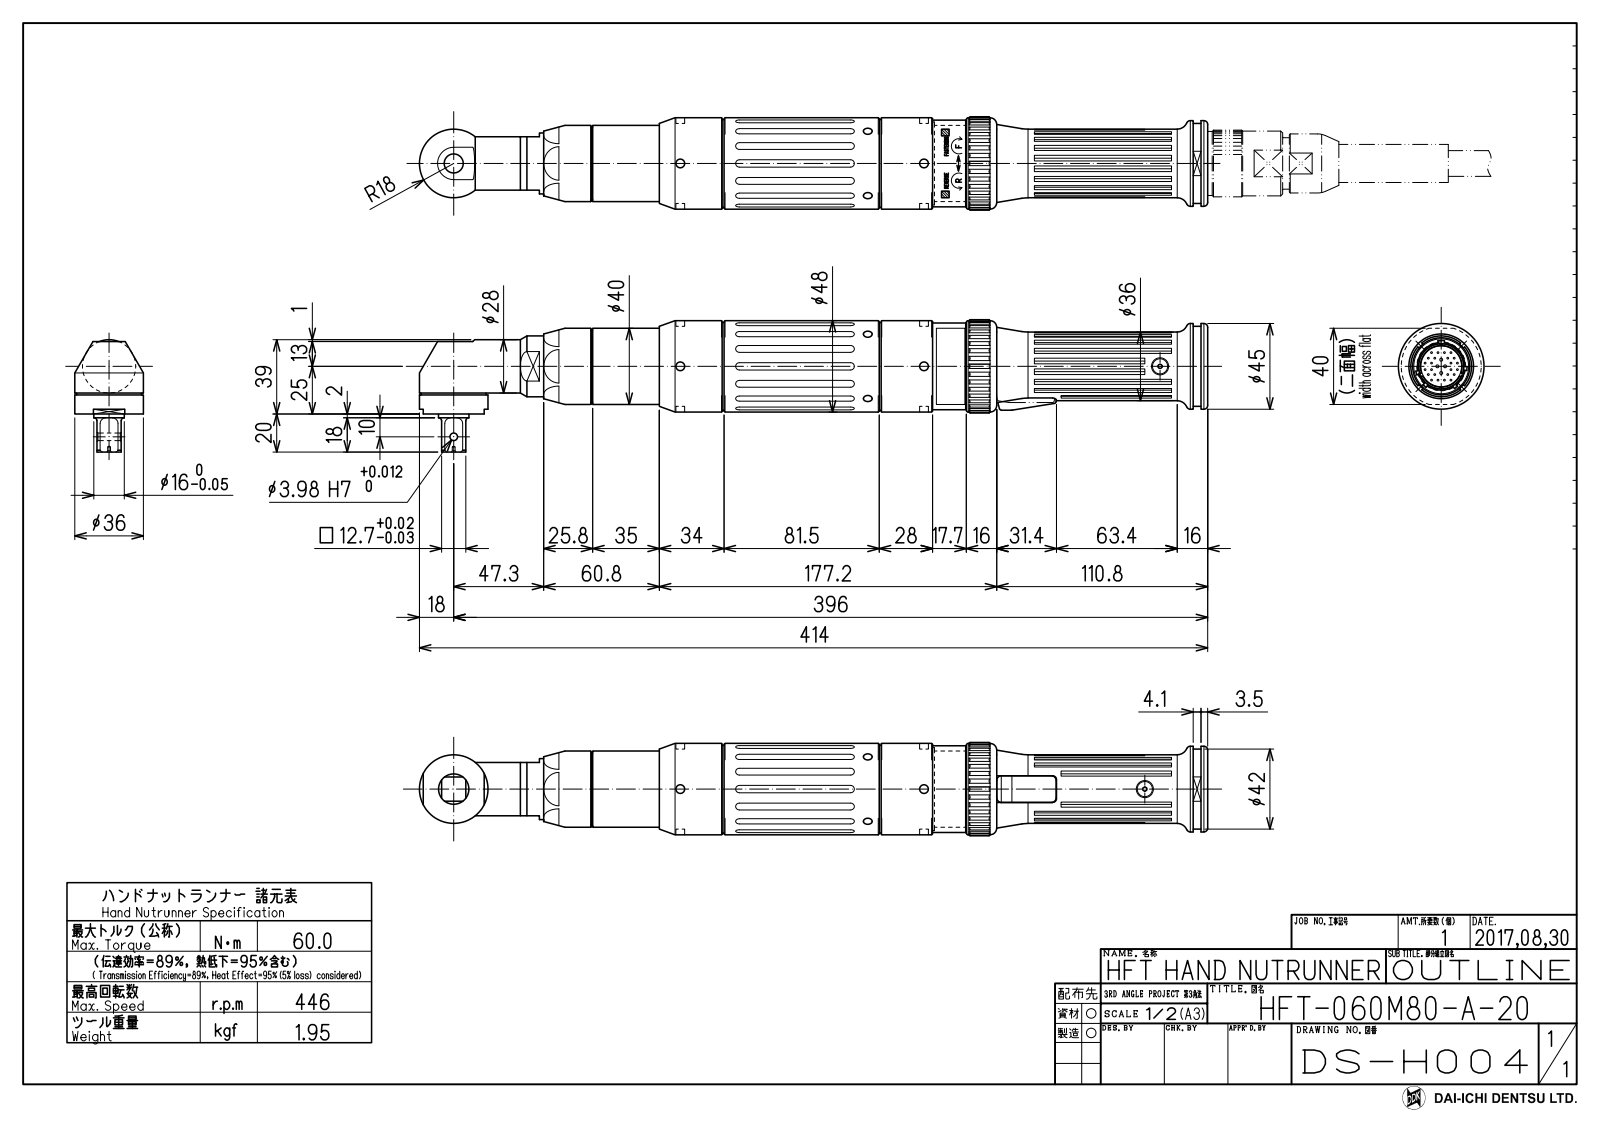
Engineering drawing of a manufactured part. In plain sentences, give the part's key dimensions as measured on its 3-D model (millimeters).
The part is named "HFT-060M80-A-20(DS-H004)_OUTLINE". Its 3-D file was written by "Autodesk Inventor 2017 (AUTOMOTIVE_DESIGN)". It is 1 solid with 947 faces: 521 planar, 276 cylindrical and 150 other. Overall it measures 414.55 by 69.58 by 49 millimeters. Its volume is 548 558 cubic millimeters and its surface area 88 899 square millimeters. Round holes: 6 of diameter 4.6, 2 of diameter 9, 1 of diameter 1.5, 1 of diameter 3, 1 of diameter 3.98, 1 of diameter 4.5, 1 of diameter 6, 1 of diameter 6.8, 1 of diameter 11, 1 of diameter 16.5, 1 of diameter 22.6, 1 of diameter 25. Round bosses or shafts: 24 of diameter 1, 4 of diameter 1.6, 2 of diameter 36, 2 of diameter 8, 2 of diameter 4, 1 of diameter 48, 1 of diameter 46, 1 of diameter 45.5. Partial cylindrical surfaces (rounded edges, fillets, slot ends): 40 of radius 1.5, 36 of radius 0.1, 22 of radius 2.5, 18 of radius 0.33, 4 of radius 3, 2 of radius 0.3, 2 of radius 0.88, 2 of radius 1. The main face-to-face distances are 34.96, 1, 28, 34, 3.48, 31.48, 15.4, 11.9, 11.13, 23.83. The hole center spacings are 128, 11, 37.08, 46.3, 57.3, 58.7, 69.7, 116.
